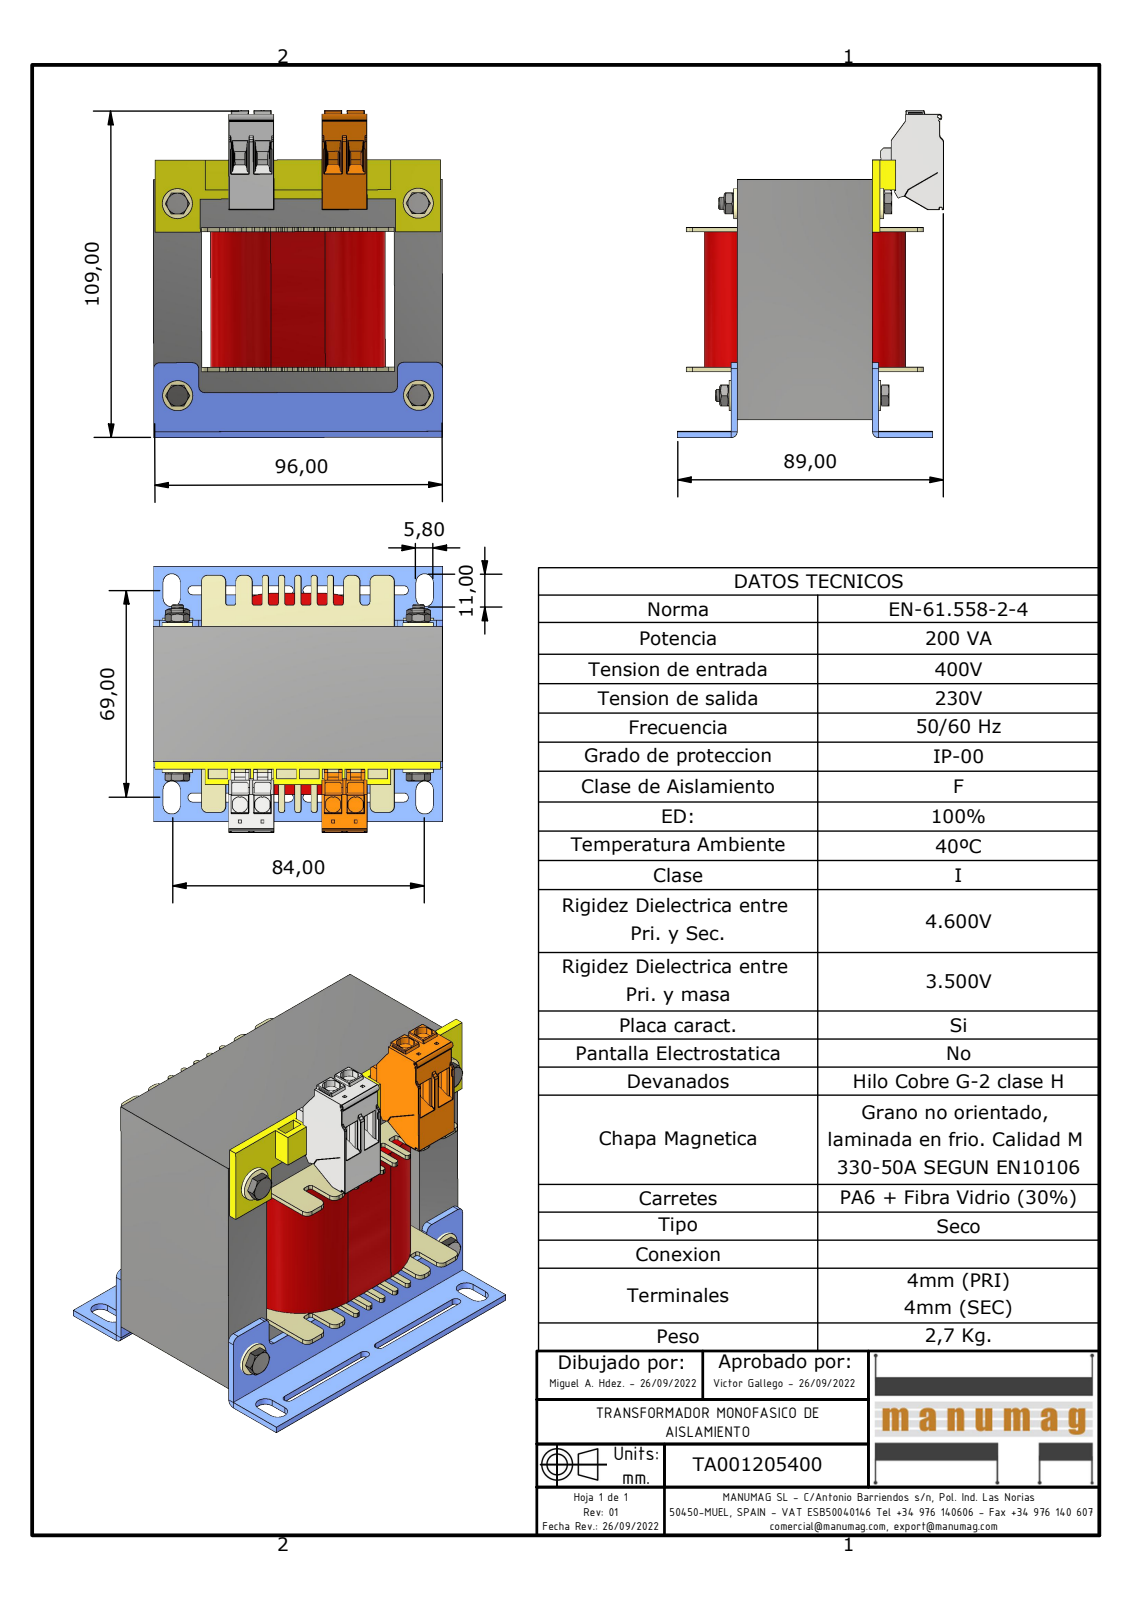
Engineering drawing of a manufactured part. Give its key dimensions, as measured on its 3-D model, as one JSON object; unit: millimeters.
{"part_name": "TA001205400; EI96 x 80 - 45 (RC32); EI96; AF32DIN (+6 more)", "step_written_by": "Autodesk Inventor 2023 (AUTOMOTIVE_DESIGN)", "units": "millimeters", "bodies": {"solids": 23, "faces": 3904, "planar": 3082, "cylindrical": 580, "other": 242}, "overall_size": [109.12, 96.14, 88.7], "volume_mm3": 407082, "surface_area_mm2": 107787, "round_holes": [[3.24, 4], [4, 4], [5.5, 4], [5.8, 2]], "round_bosses_or_shafts": [[10, 4], [5.9, 4], [4.9, 4], [3.62, 4]], "partial_cylinders_radius": [[0.15, 162], [0.8, 102], [0.2, 60], [2, 38], [0.5, 17], [0.3, 14], [1, 8], [1.5, 8]], "face_to_face_distances": [45, 48, 64.02, 2, 16.02, 32, 16.01, 15.98, 80.03, 64.01], "hole_center_spacings": [64, 80, 102.45]}
